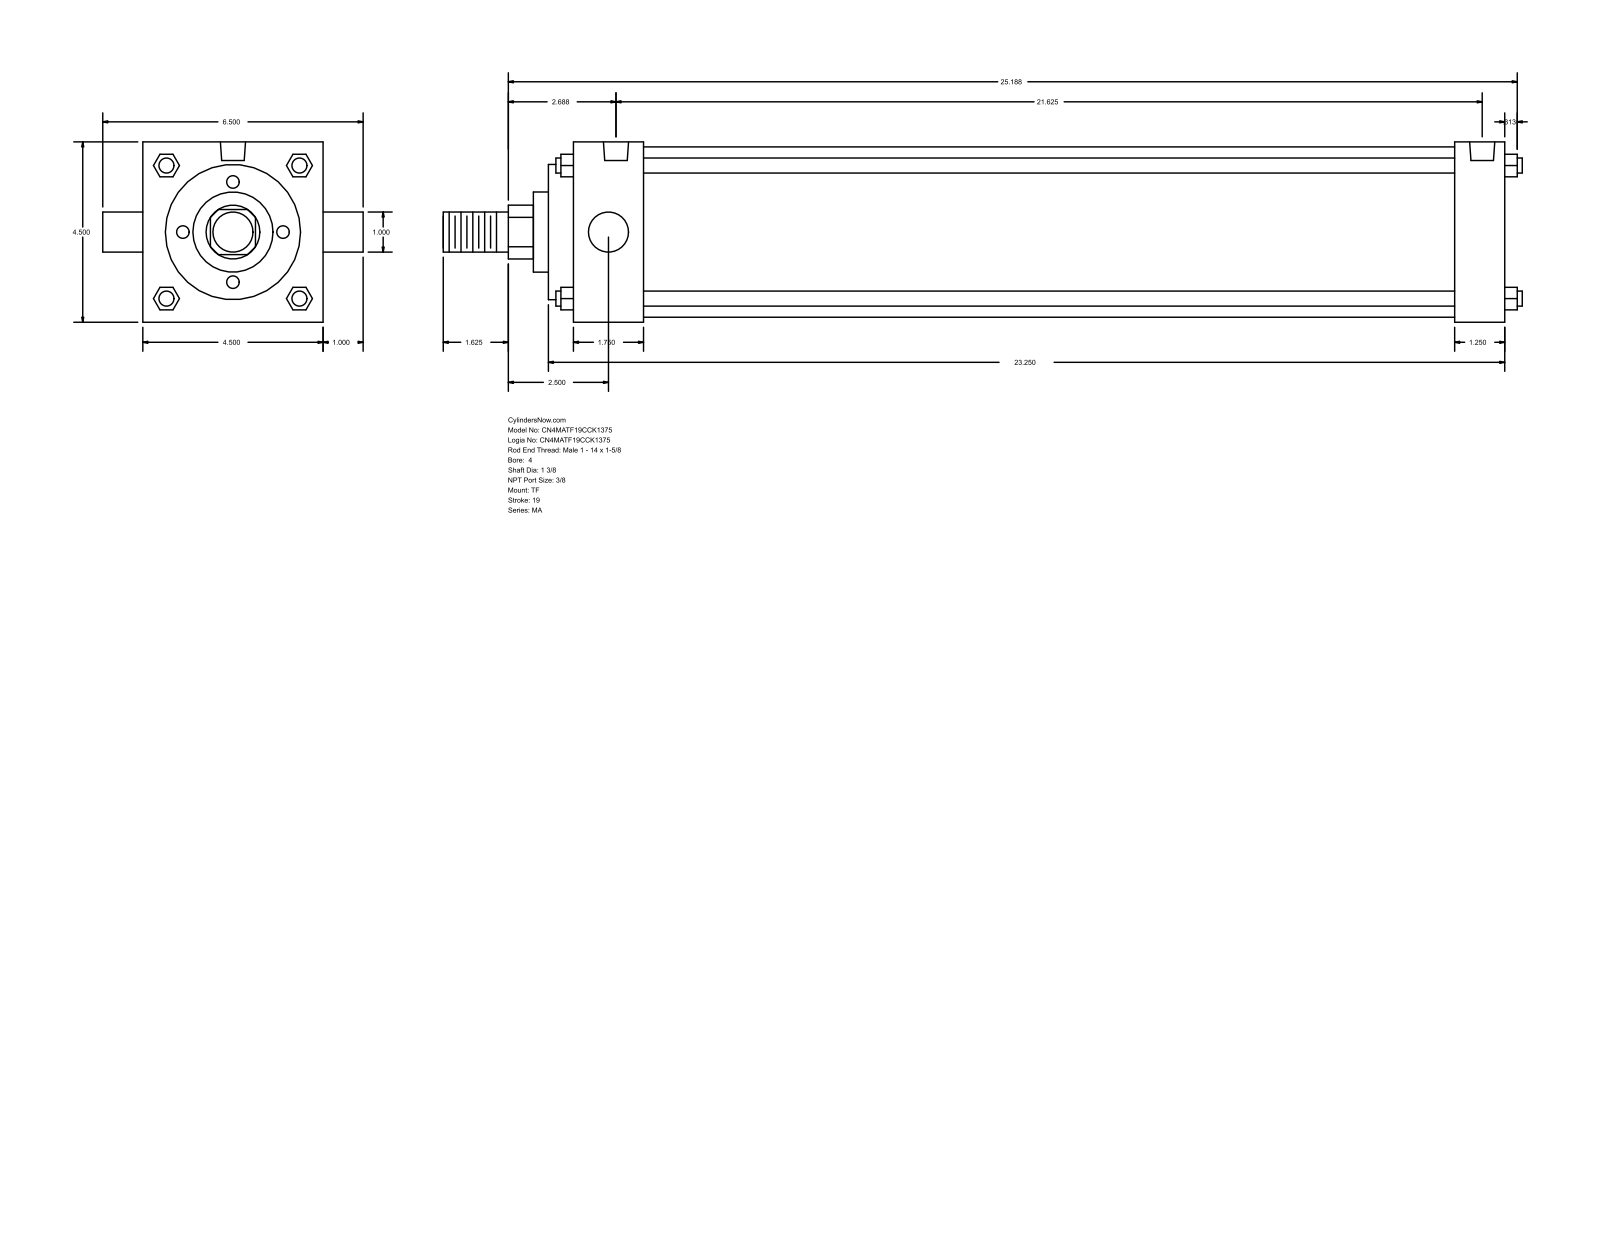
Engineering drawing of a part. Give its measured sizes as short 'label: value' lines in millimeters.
name: MA_TF__0400_1.375
written by: GSSL Pune (CONFIG_CONTROL_DESIGN)
unit: mm
bodies: 0 solids, 122 faces (93 planar, 29 cylindrical, 0 other)
size: 684.21 × 165.1 × 114.3
holes: 3× ⌀11.11, 2× ⌀15.93
bosses: 4× ⌀9.53, 2× ⌀25.4, 1× ⌀107.95, 1× ⌀85.72, 1× ⌀50.8, 1× ⌀34.92
rounds: 1× R17.06
face distances: 114.3, 590.56, 15.87, 606.43, 574.68, 558.81, 31.75, 60.32, 44.45, 514.36
hole spacings: 4.77, 544.51, 539.74, 549.28
